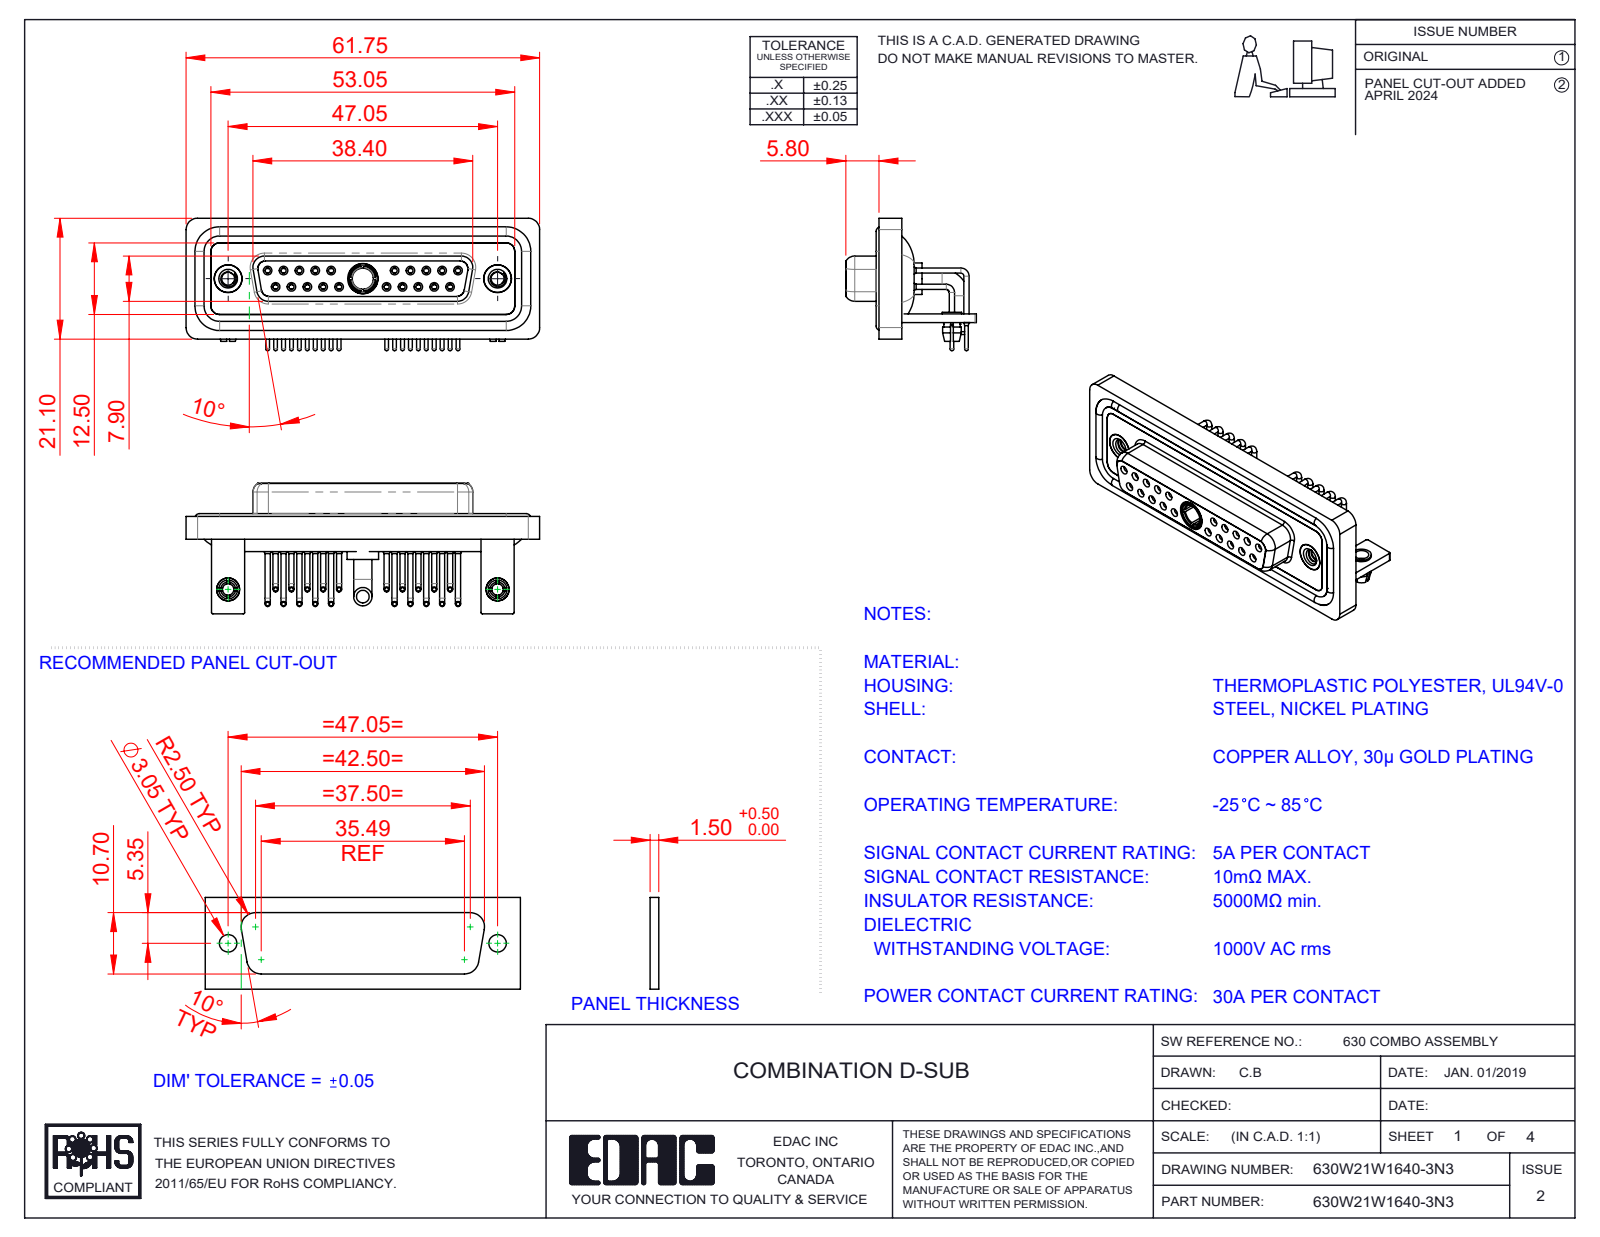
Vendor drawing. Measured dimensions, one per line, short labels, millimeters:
name: 630Combo Board Lock_50 Contacts; 630Combo Housing_21W1; 630Combo Threaded Rivet_2; 630Combo Shell Rear_25 Contacts (+7 more)
written by: SolidWorks 2023 (CONFIG_CONTROL_DESIGN)
unit: mm
bodies: 33 solids, 1664 faces (502 planar, 729 cylindrical, 433 other)
size: 61.75 × 23.12 × 22.8
volume: 8 936 mm³; area: 15 744 mm²
holes: 22× ⌀2, 20× ⌀0.9, 20× ⌀1.1, 20× ⌀1.5, 10× ⌀1.6, 10× ⌀1.7, 3× ⌀4.85, 2× ⌀2.26, 2× ⌀2.5, 2× ⌀3.2, 2× ⌀4, 2× ⌀4.05
bosses: 20× ⌀0.9, 20× ⌀0.65, 14× ⌀1.6, 2× ⌀4.95, 2× ⌀4.8, 2× ⌀4, 2× ⌀3.4, 2× ⌀3.3
rounds: 19× R2, 18× R1.5, 16× R0.25, 8× R1.35, 8× R1.6, 5× R0.5, 4× R0.6, 4× R0.65
face distances: 0.4, 1.8, 2.9, 3.7, 1.5, 4.1, 1.1, 1.4, 1.6, 2.5
hole spacings: 3.16, 2.77, 5.54, 8.31, 5.04, 19.39, 20.97, 22.16
